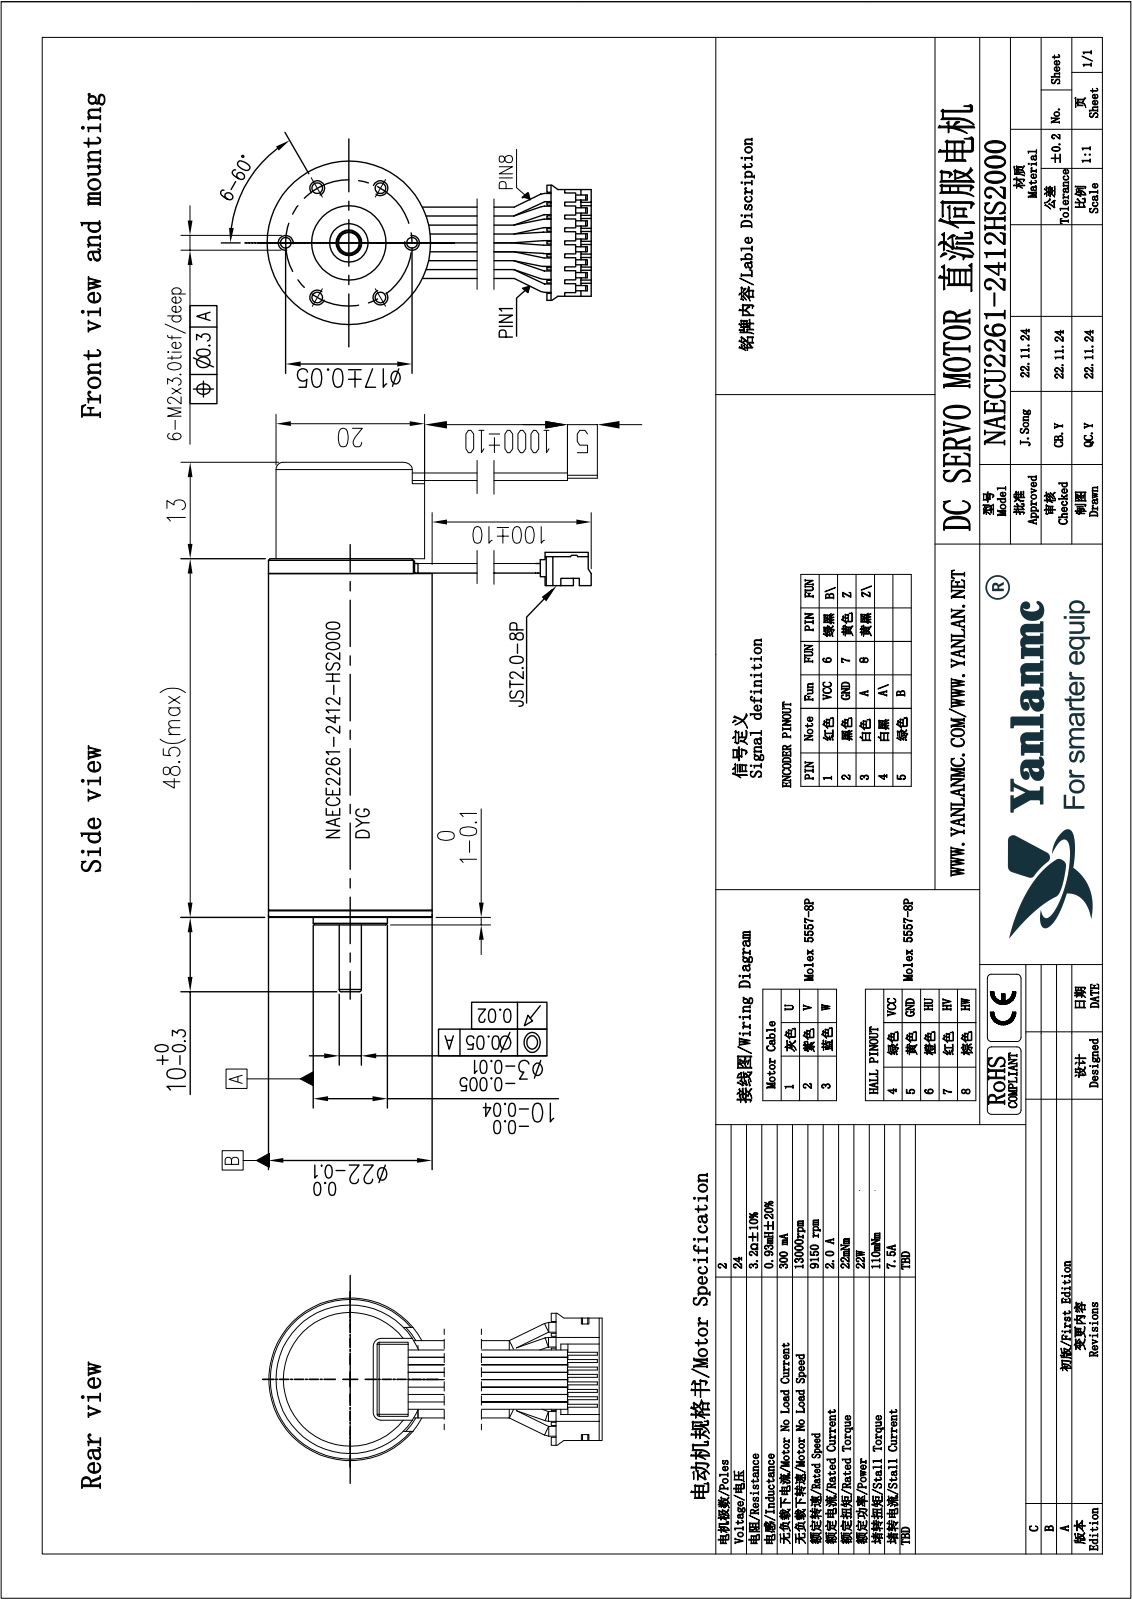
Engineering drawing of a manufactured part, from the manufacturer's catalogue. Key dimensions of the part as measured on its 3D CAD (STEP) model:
STEP written by: SolidWorks 2020 (AUTOMOTIVE_DESIGN)
Units: millimetres
Bodies: 19 solids, 147 faces (60 planar, 71 cylindrical, 16 other)
Overall size (bounding box): 71.5 × 34.03 × 22
Volume: 22 704 mm³ · Surface area: 6 606 mm²
Round holes (diameter × count): ⌀1.6 ×6
Round bosses / shafts (diameter × count): ⌀0.9 ×16, ⌀0.59 ×8, ⌀22 ×1, ⌀20 ×1, ⌀10 ×1, ⌀3 ×1
Main face-to-face distances: 13, 48.5, 61.5, 2, 1, 49.5, 62.5, 47.5, 46.5, 15
Hole centre spacings: 8.5, 14.72, 17
